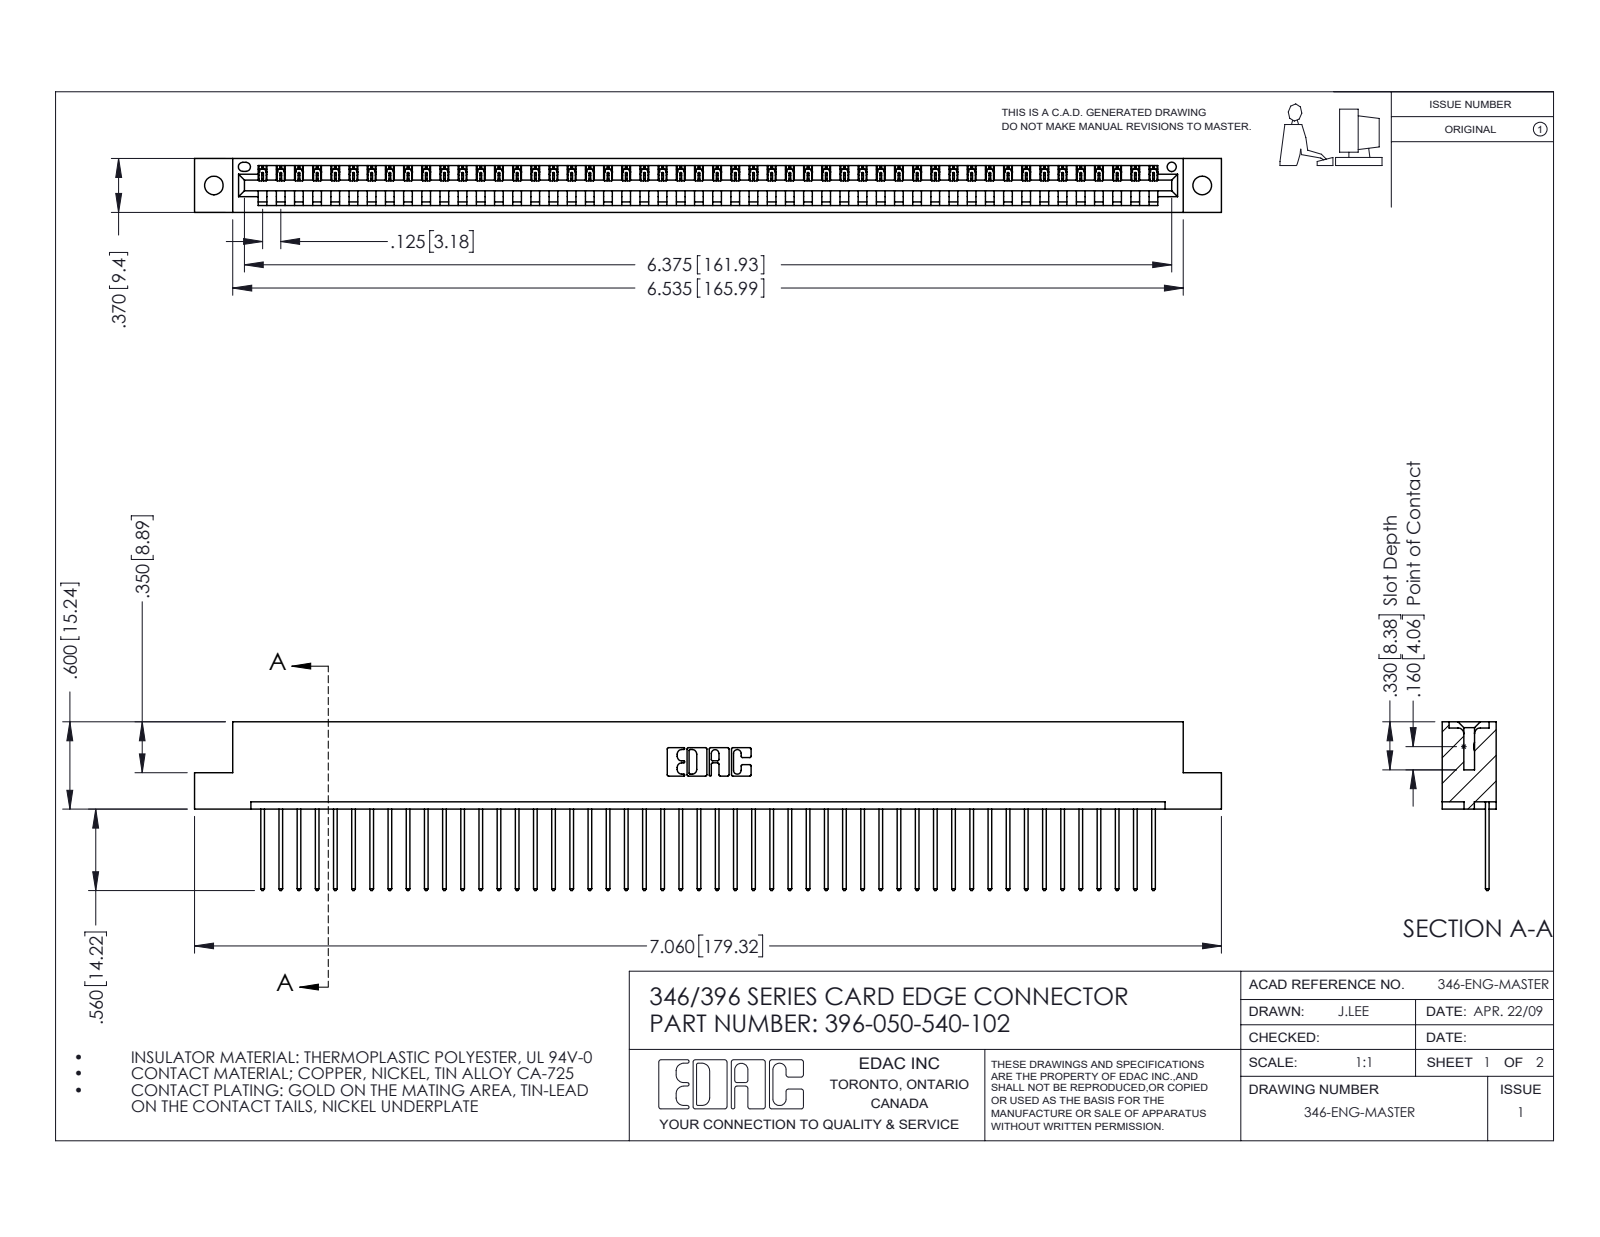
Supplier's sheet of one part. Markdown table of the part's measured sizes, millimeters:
| quantity | value |
| --- | --- |
| part name | 345-292-001_345-293-140; 346 Part_Flush Mounting Lugs - 0.128 Dia; 396-050-540-102 |
| STEP written by | SolidWorks 2016 (CONFIG_CONTROL_DESIGN) |
| units | millimeters |
| bodies | 51 solids, 3022 faces (2076 planar, 946 cylindrical, 0 other) |
| overall size | 179.3 × 29.5 × 9.4 |
| volume | 17 260 mm³ |
| surface area | 21 870 mm² |
| round holes (diameter × count) | 3.3 × 2, 1.6 × 1 |
| partial cylindrical surfaces (radius × count) | 0.2 × 100, 0.3 × 100, 0.3 × 22, 0.2 × 6, 0.8 × 6, 0.7 × 3, 0.8 × 2, 1 × 2 |
| main face-to-face distances | 1.2, 8.2, 9.4, 6.4, 1.8, 7.6, 0.6, 3.8, 5.6, 2.5 |
| hole center spacings | 6.2, 167.3, 172.6 |
